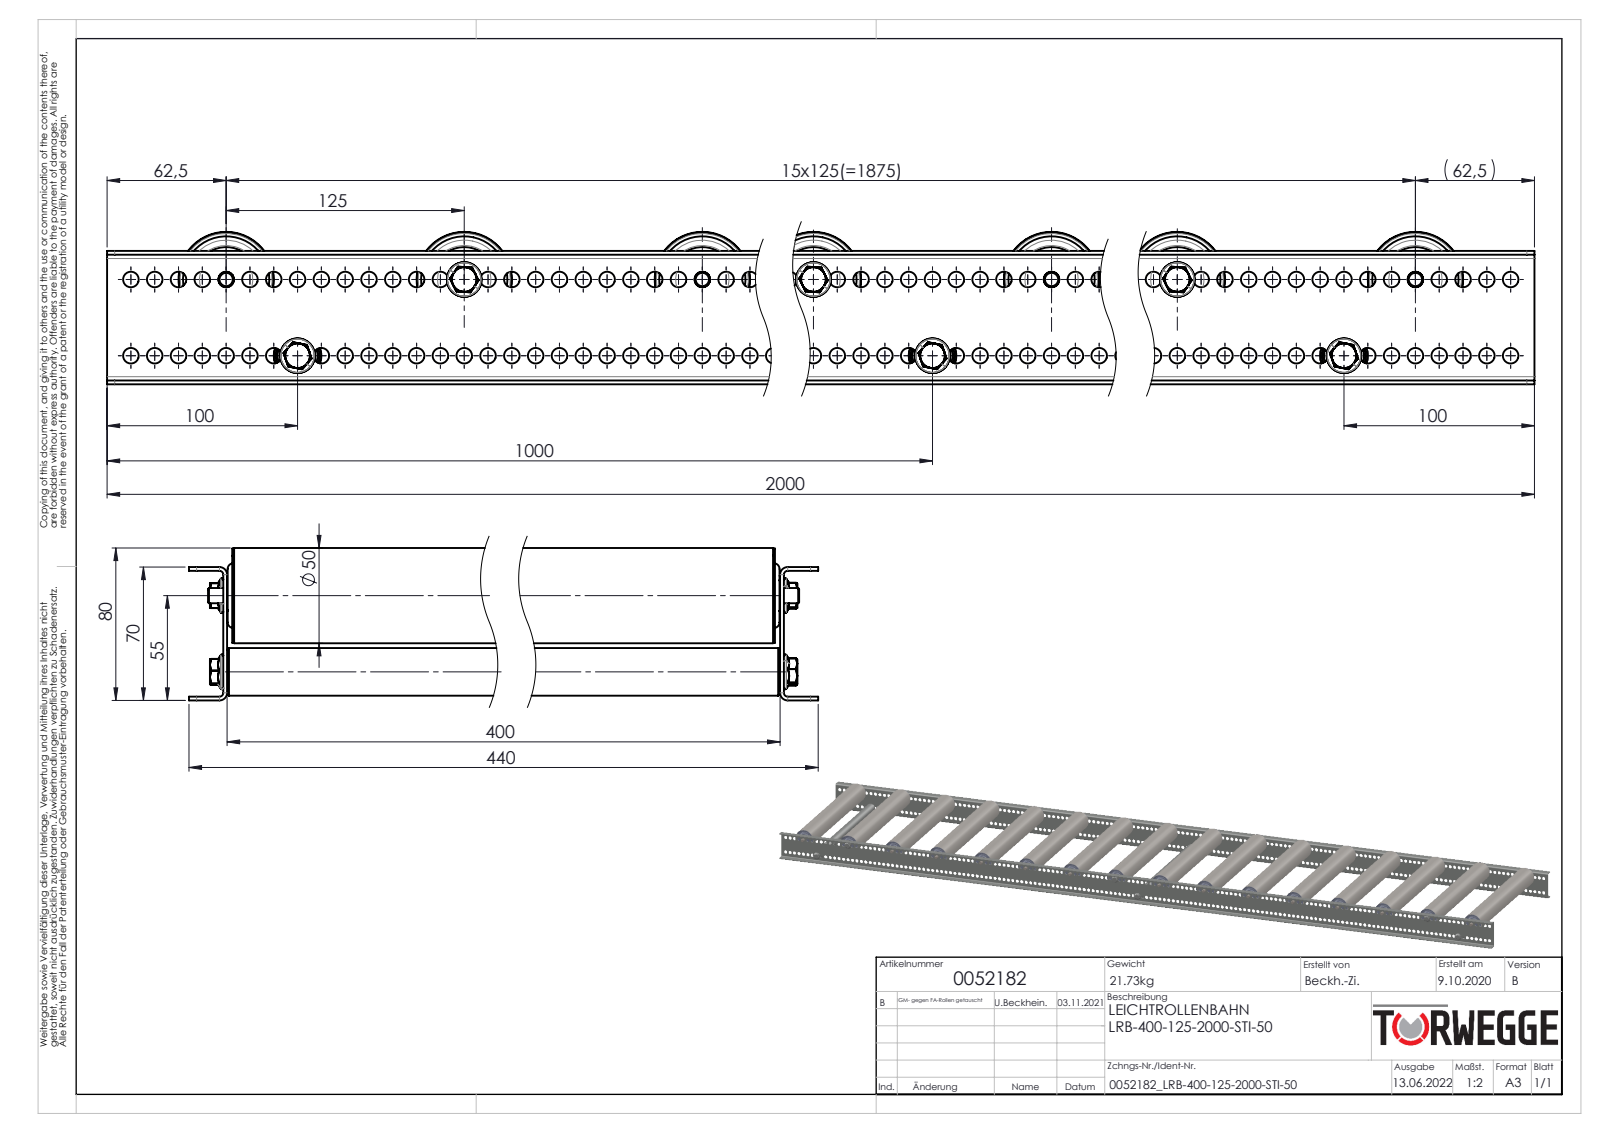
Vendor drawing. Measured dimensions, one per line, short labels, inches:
name: 0026295_Typ-TRG_50x1,5-8; 0039771_Tragrollenrohr-Ø50x1,5STI_KFG_EL400; 0026293_Typ-TRG-50x1,5-12; S100994_Sperrzahnschraube_M08x16-8.8-A2K (+8 more)
written by: SolidWorks 2020 (AUTOMOTIVE_DESIGN)
unit: in
bodies: 392 solids, 7558 faces (1452 planar, 2944 cylindrical, 3162 other)
size: 78.74 × 17.323 × 3.15
volume: 189.8 in³; area: 5 540 in²
holes: 318× ⌀0.323, 16× ⌀0.673, 16× ⌀0.728, 16× ⌀1.091, 16× ⌀1.783, 16× ⌀1.85, 13× ⌀0.299, 6× ⌀0.268, 3× ⌀0.472, 3× ⌀0.48, 3× ⌀0.756, 3× ⌀0.827
bosses: 19× ⌀0.315, 16× ⌀1.969, 16× ⌀1.949, 16× ⌀1.862, 16× ⌀1.169, 16× ⌀1.079, 16× ⌀1.075, 16× ⌀0.63
rounds: 26× R0.024, 26× R0.03, 26× R0.096, 13× R0.192, 13× R0.276, 12× R0.098, 8× R0.157, 4× R0.079
face distances: 0.079, 15.827, 2.677, 15.748, 15.906, 2.756, 2.598, 0.039, 0.787, 0.709
hole spacings: 0.492, 0.984, 1.476, 1.969, 2.461, 2.953, 3.445, 3.937
